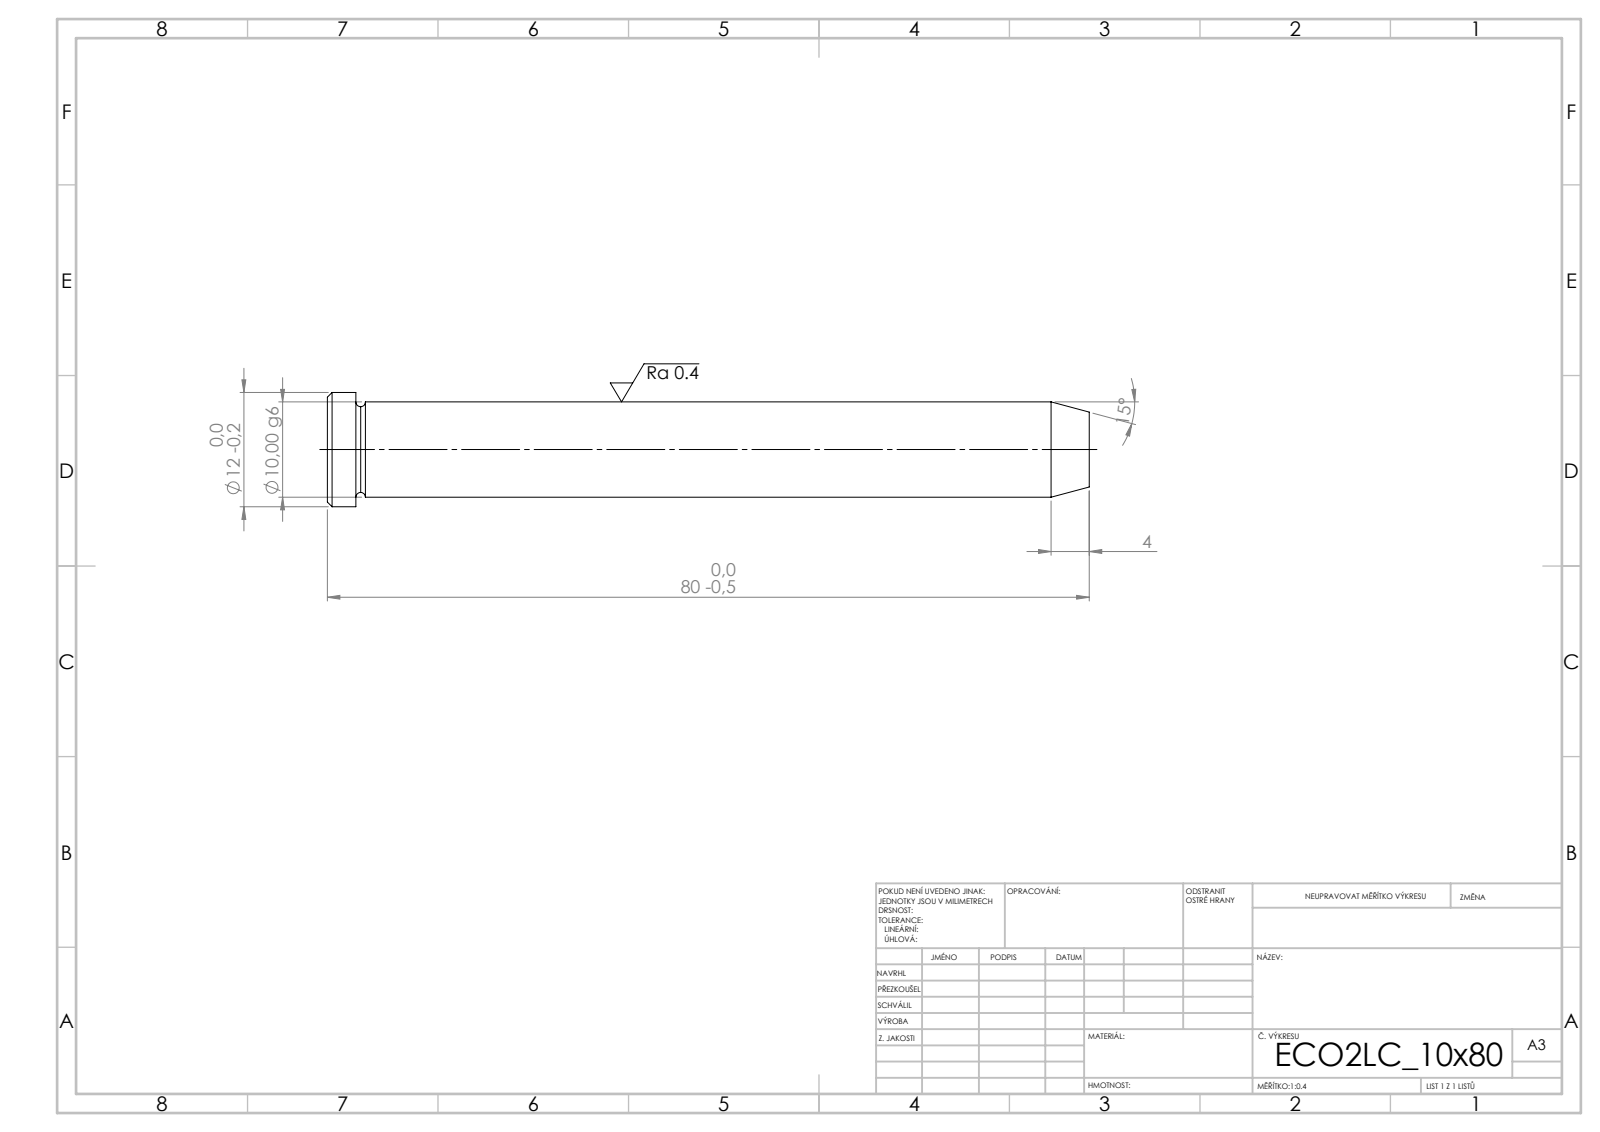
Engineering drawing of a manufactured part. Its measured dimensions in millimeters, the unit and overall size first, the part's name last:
Units: millimetres
Overall size (bounding box): 80 × 12 × 12
Round bosses / shafts (diameter × count): ⌀12 ×1, ⌀10 ×1
Main face-to-face distances: 80, 77, 3
Volume: 6 308 mm³ · Surface area: 2 722 mm²
Bodies: 1 solid, 15 faces (3 planar, 4 cylindrical, 8 other)
STEP written by: SolidWorks 2019 (CONFIG_CONTROL_DESIGN)
